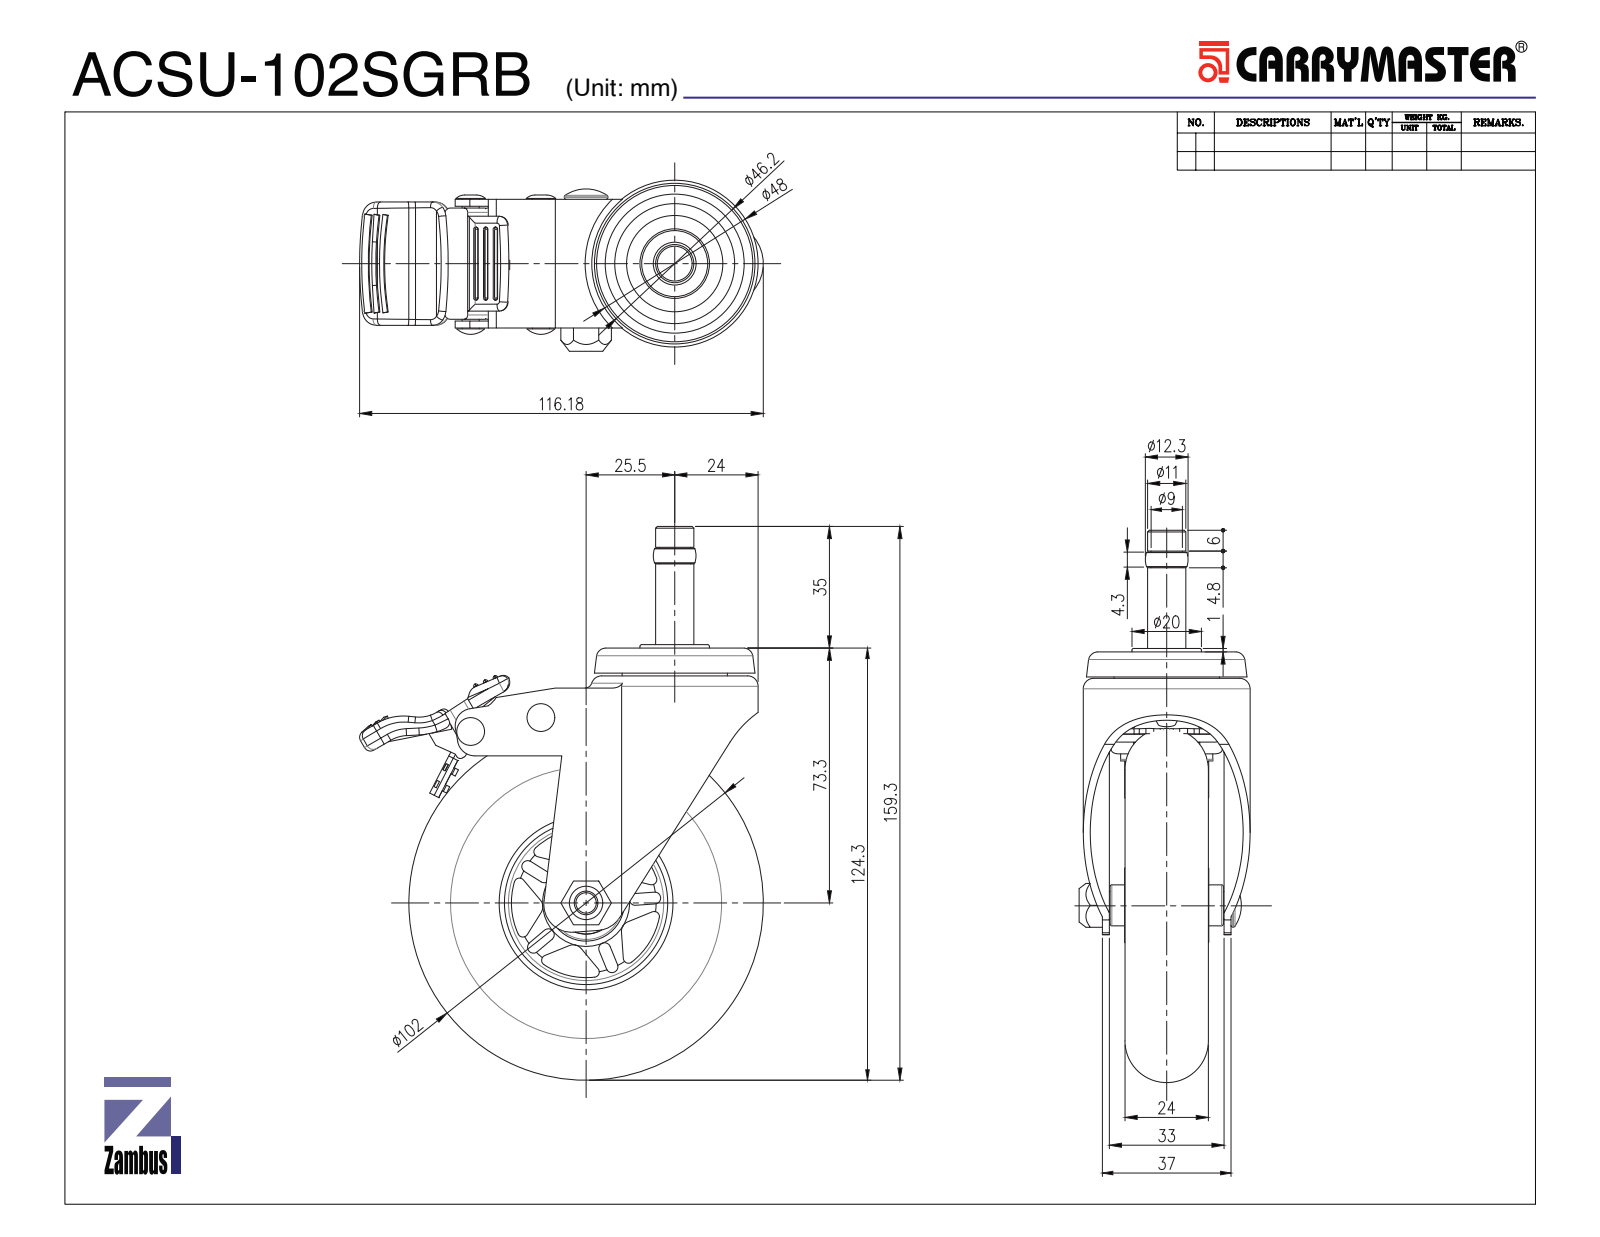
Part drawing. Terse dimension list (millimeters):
name: 102RF_102RFACSU-102 CORE; ACSU-102SFB BRAKE PLATE; ACSU-102SFB BODY; ACSU-102SFB BRAKE (+8 more)
written by: SolidWorks 2016 (AUTOMOTIVE_DESIGN)
unit: mm
bodies: 28 solids, 953 faces (364 planar, 361 cylindrical, 228 other)
size: 158.9 × 116.18 × 49.2
volume: 217 763 mm³; area: 92 966 mm²
holes: 2× ⌀3.5, 2× ⌀4, 1× ⌀6.8, 1× ⌀8, 1× ⌀8.1, 1× ⌀10, 1× ⌀11, 1× ⌀11.9, 1× ⌀18, 1× ⌀18.5, 1× ⌀22, 1× ⌀26.3
bosses: 2× ⌀4.9, 1× ⌀42.4, 1× ⌀30.3, 1× ⌀20, 1× ⌀18, 1× ⌀17.9, 1× ⌀16, 1× ⌀12.5
rounds: 45× R1, 20× R0.6, 14× R1.5, 13× R2, 12× R1.7, 8× R3, 6× R0.5, 5× R2.5
face distances: 2, 6.5, 30.5, 4.5, 35, 28.5, 24, 3.5, 1.5, 37
hole spacings: 4.94, 20.61, 54.86, 59.45
